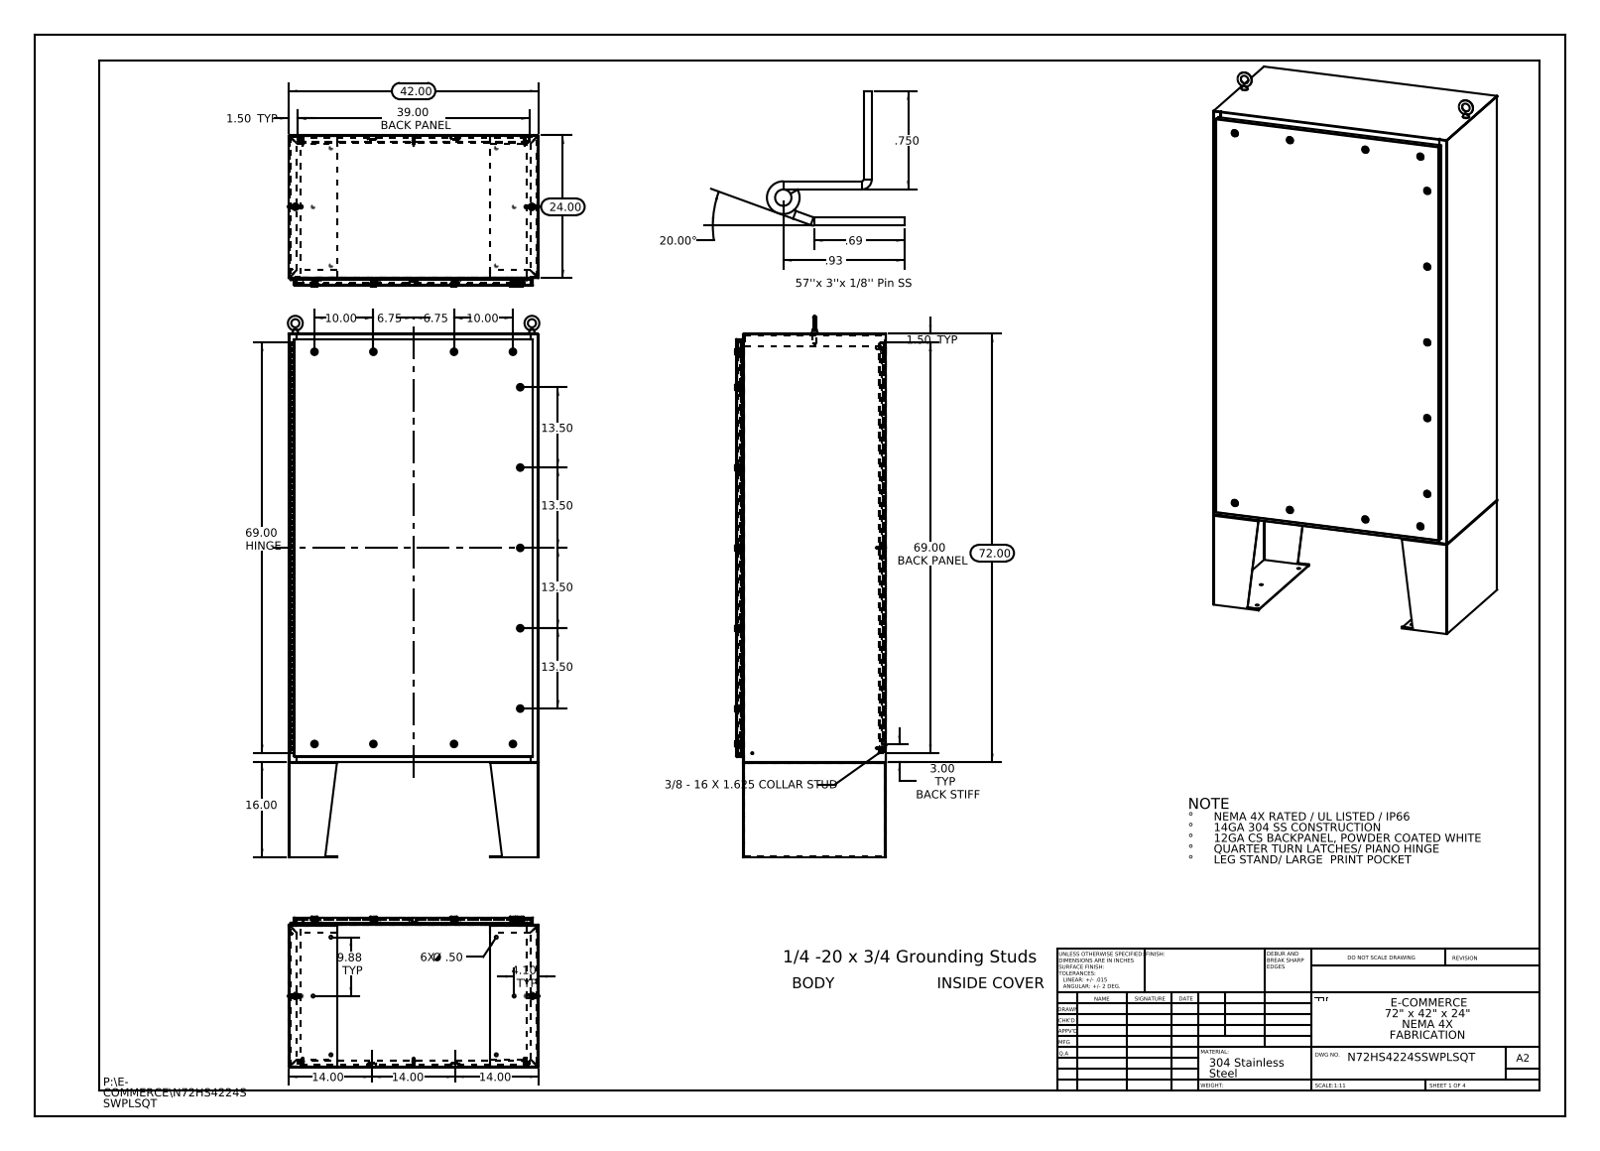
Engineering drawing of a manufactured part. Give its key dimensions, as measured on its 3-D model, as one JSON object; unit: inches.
{"part_name": "N72HS4224SSWPLSQT Backpanel; N72HS4224SSWPLSQT Door Stiffener; N72HS4224SSWPLSQT SD-LSK-ASSY; N72HS4224SSWPLSQT 125 Pin Hinge (+8 more)", "step_written_by": "SolidWorks 2013 (CONFIG_CONTROL_DESIGN)", "units": "inches", "bodies": {"solids": 36, "faces": 2647, "planar": 1331, "cylindrical": 1120, "other": 196}, "overall_size": [91, 42.271, 25.201], "volume_in3": 1459, "surface_area_in2": 35394, "round_holes": [[0.5, 14], [0.25, 8], [0.75, 4], [0.125, 1], [0.125, 1]], "round_bosses_or_shafts": [[0.625, 10], [0.375, 8], [0.33, 8], [0.157, 8], [0.14, 8], [0.315, 2], [0.236, 2], [0.25, 1]], "partial_cylinders_radius": [[0.013, 36], [0.088, 30], [0.039, 8], [0.143, 8], [0.442, 8], [0.019, 6], [0.117, 4], [0.125, 4]], "face_to_face_distances": [0.075, 25.126, 0.104, 41.925, 25.051, 1.075, 25.201, 24.126, 1, 24.051], "hole_center_spacings": [2.225, 10.324, 11.553, 33.625, 35.196, 38.439, 50.181, 69.781]}
